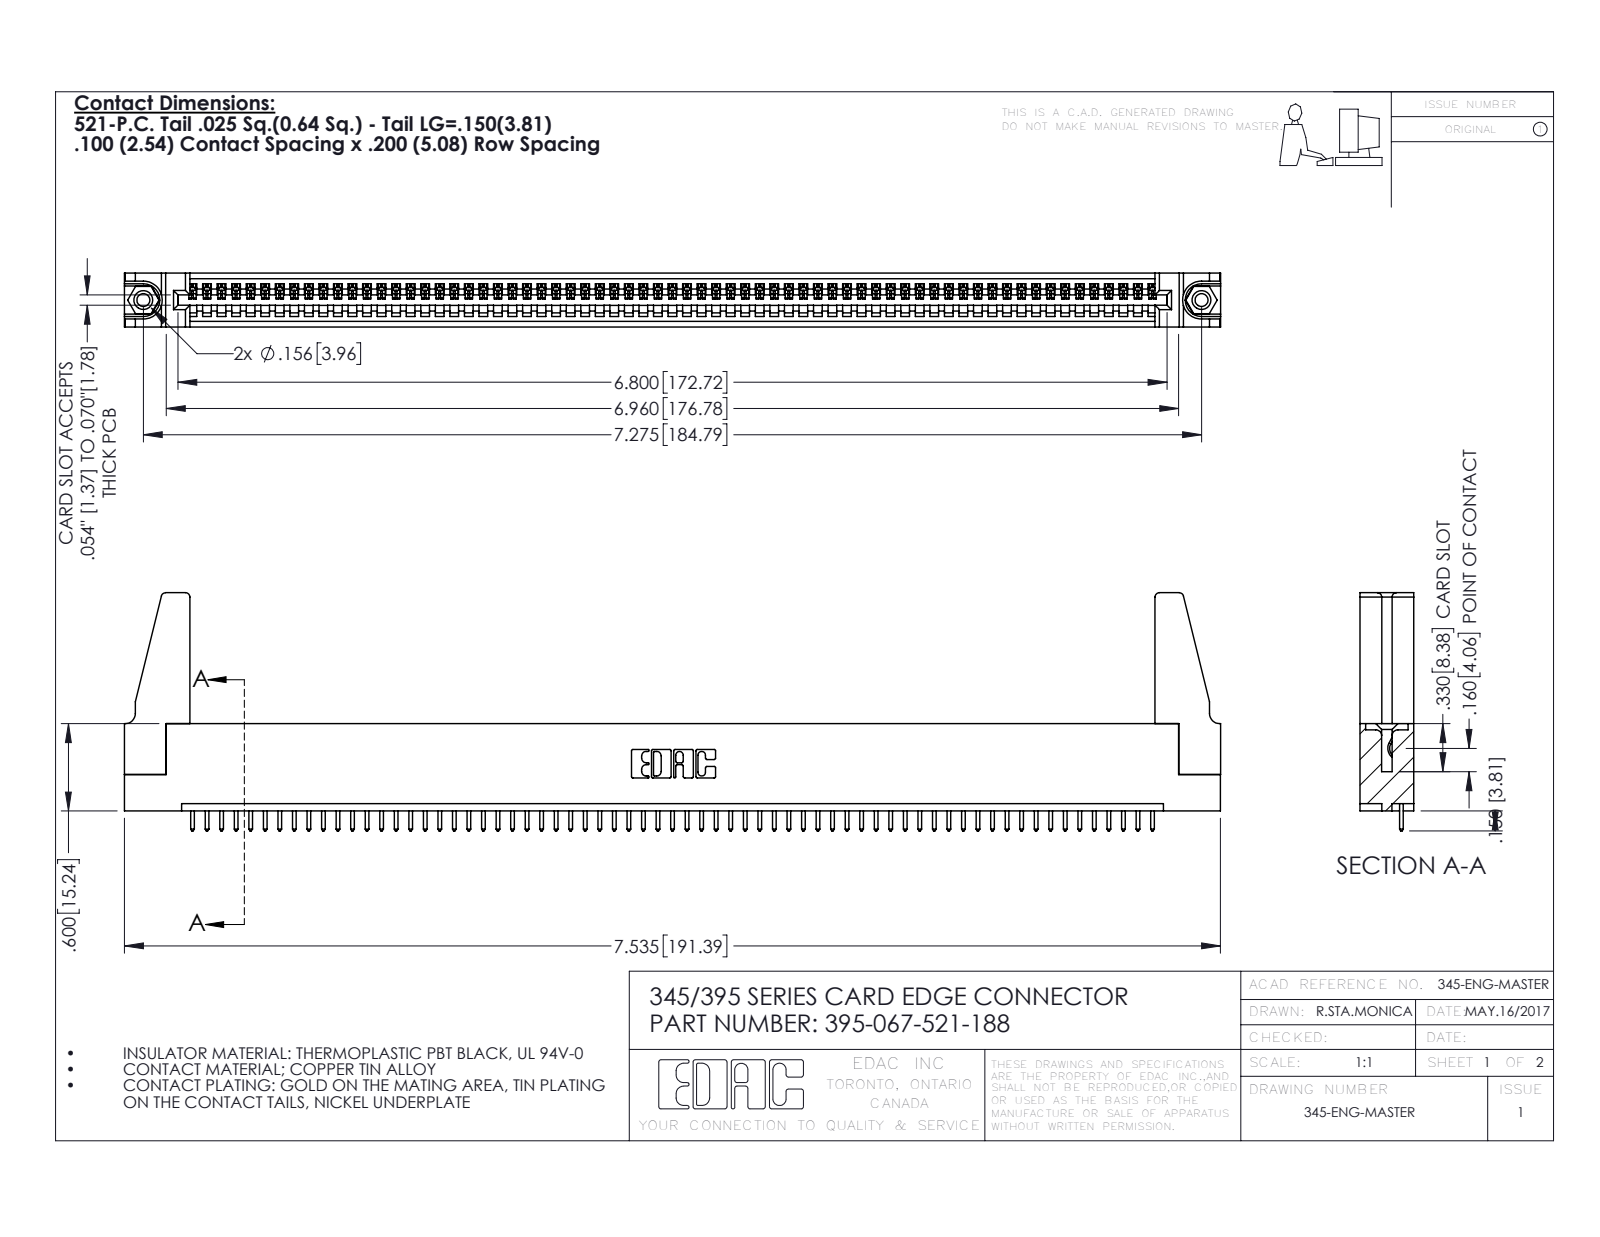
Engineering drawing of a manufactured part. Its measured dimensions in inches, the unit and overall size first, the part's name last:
Units: inches
Overall size (bounding box): 7.536 × 1.637 × 0.37
Round holes (diameter × count): ⌀0.089 ×2, ⌀0.125 ×2, ⌀0.156 ×2, ⌀0.064 ×1
Round bosses / shafts (diameter × count): ⌀0.155 ×2
Partial cylindrical surfaces — rounded edges, fillets, slot ends (radius × count): R0.006 ×134, R0.01 ×134, R0.01 ×22, R0.03 ×8, R0.007 ×6, R0.031 ×6, R0.026 ×3, R0.031 ×2
Main face-to-face distances: 0.072, 0.298, 0.37, 0.2, 0.098, 0.272, 0.025, 0.225, 0.149, 0.072
Hole centre spacings: 0.27, 7.039, 7.275
Volume: 1.309 in³ · Surface area: 41.7 in²
Bodies: 72 solids, 4136 faces (2832 planar, 1288 cylindrical, 16 other)
Part name (STEP PRODUCT): 345 Part_Flush Mounting Lugs - 0.156 Dia-TH; 345-250-001_345-250-001-102; 345-292-001_345-293-121; 395-067-521-188 (+1 more)
STEP written by: SolidWorks 2016 (CONFIG_CONTROL_DESIGN)
